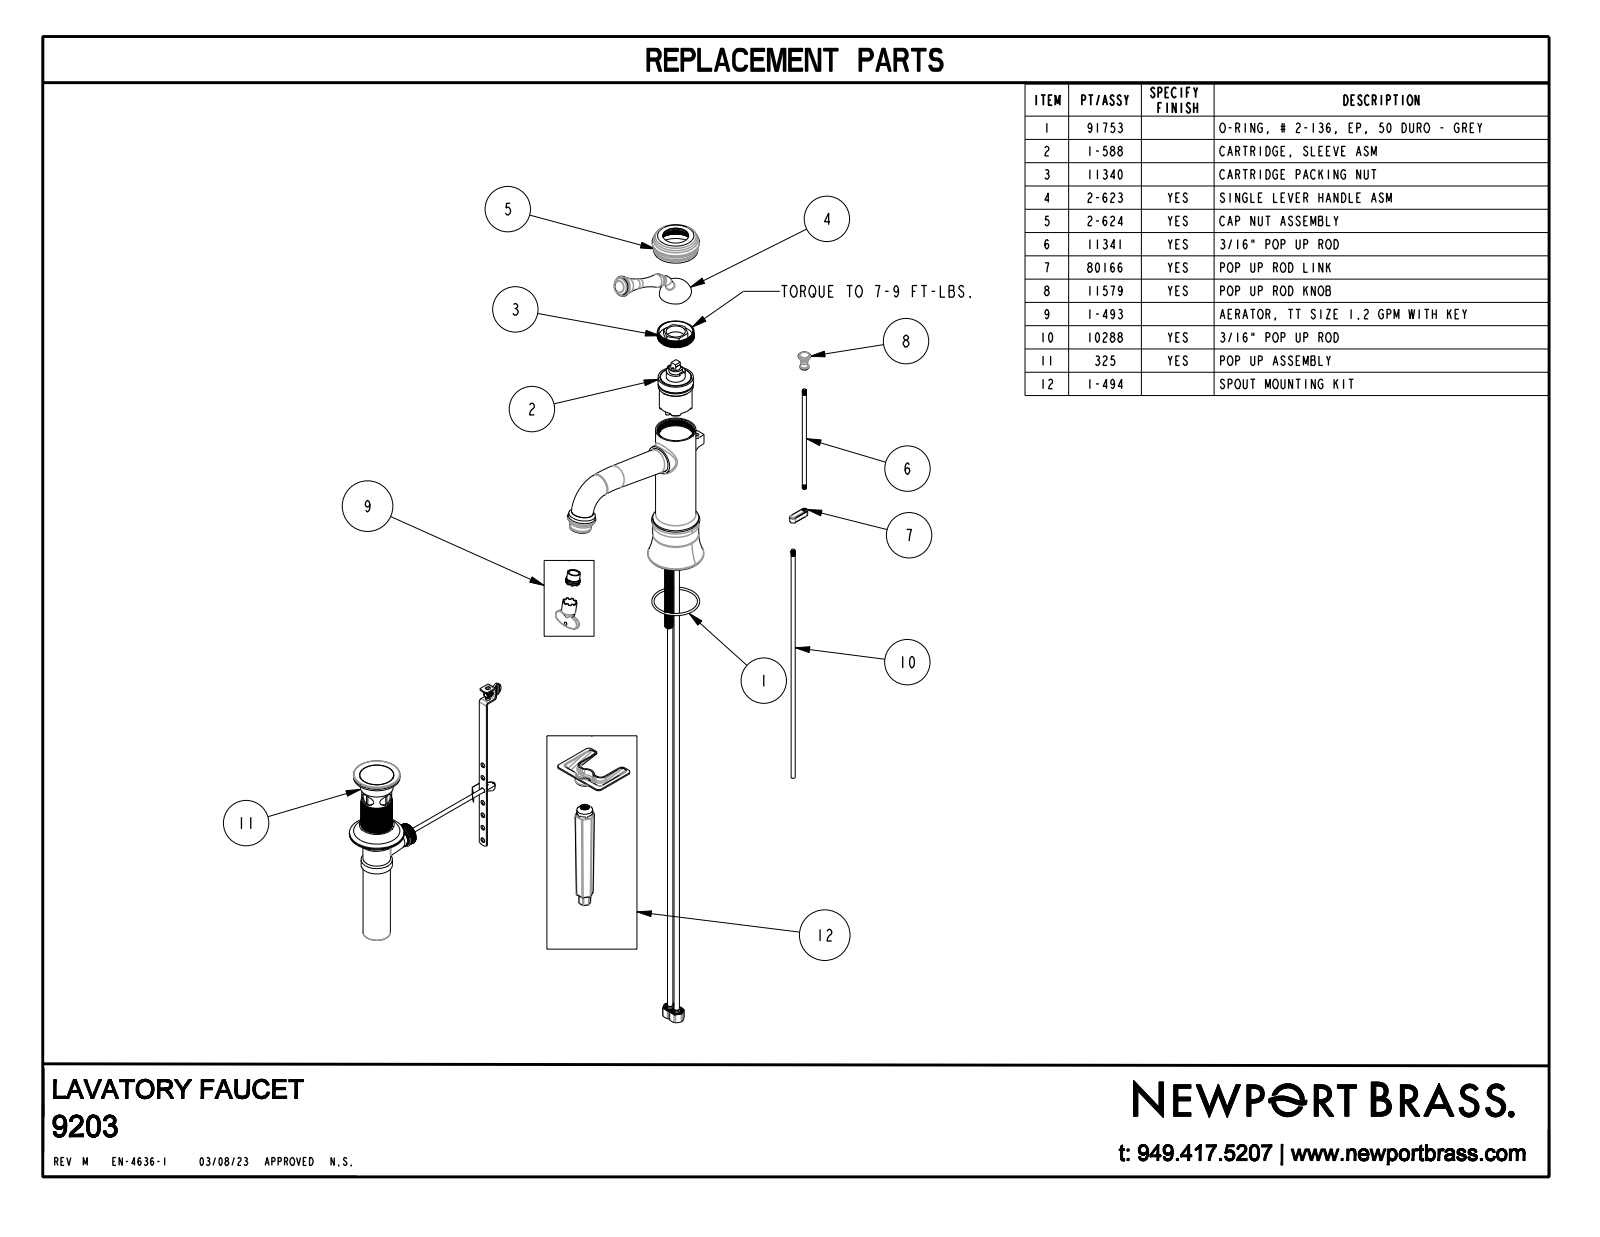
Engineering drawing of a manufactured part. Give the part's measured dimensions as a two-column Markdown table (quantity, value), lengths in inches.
| quantity | value |
| --- | --- |
| part name | 9203_SW0001 |
| STEP written by | CREO PARAMETRIC BY PTC INC, 2018400 (AUTOMOTIVE_DESIGN) |
| units | inches |
| bodies | 1 solid, 246 faces (50 planar, 62 cylindrical, 134 other) |
| overall size | 9.65 × 8.384 × 2.566 |
| volume | 29.86 in³ |
| surface area | 103.5 in² |
| round holes (diameter × count) | 0.136 × 1, 0.195 × 1, 0.205 × 1, 0.295 × 1 |
| round bosses / shafts (diameter × count) | 0.38 × 2, 2.11 × 1, 1.961 × 1, 1.85 × 1, 1.36 × 1, 1.23 × 1, 1.12 × 1, 0.788 × 1 |
| partial cylindrical surfaces (radius × count) | 0.02 × 4, 0.031 × 4, 0.04 × 2, 0.125 × 2, 0.155 × 2, 0.24 × 2, 0.195 × 1, 0.812 × 1 |
| main face-to-face distances | 7.557, 6.719, 0.839, 0.39, 1.471, 0.031, 1.502, 5.144, 1.574, 2.413 |
